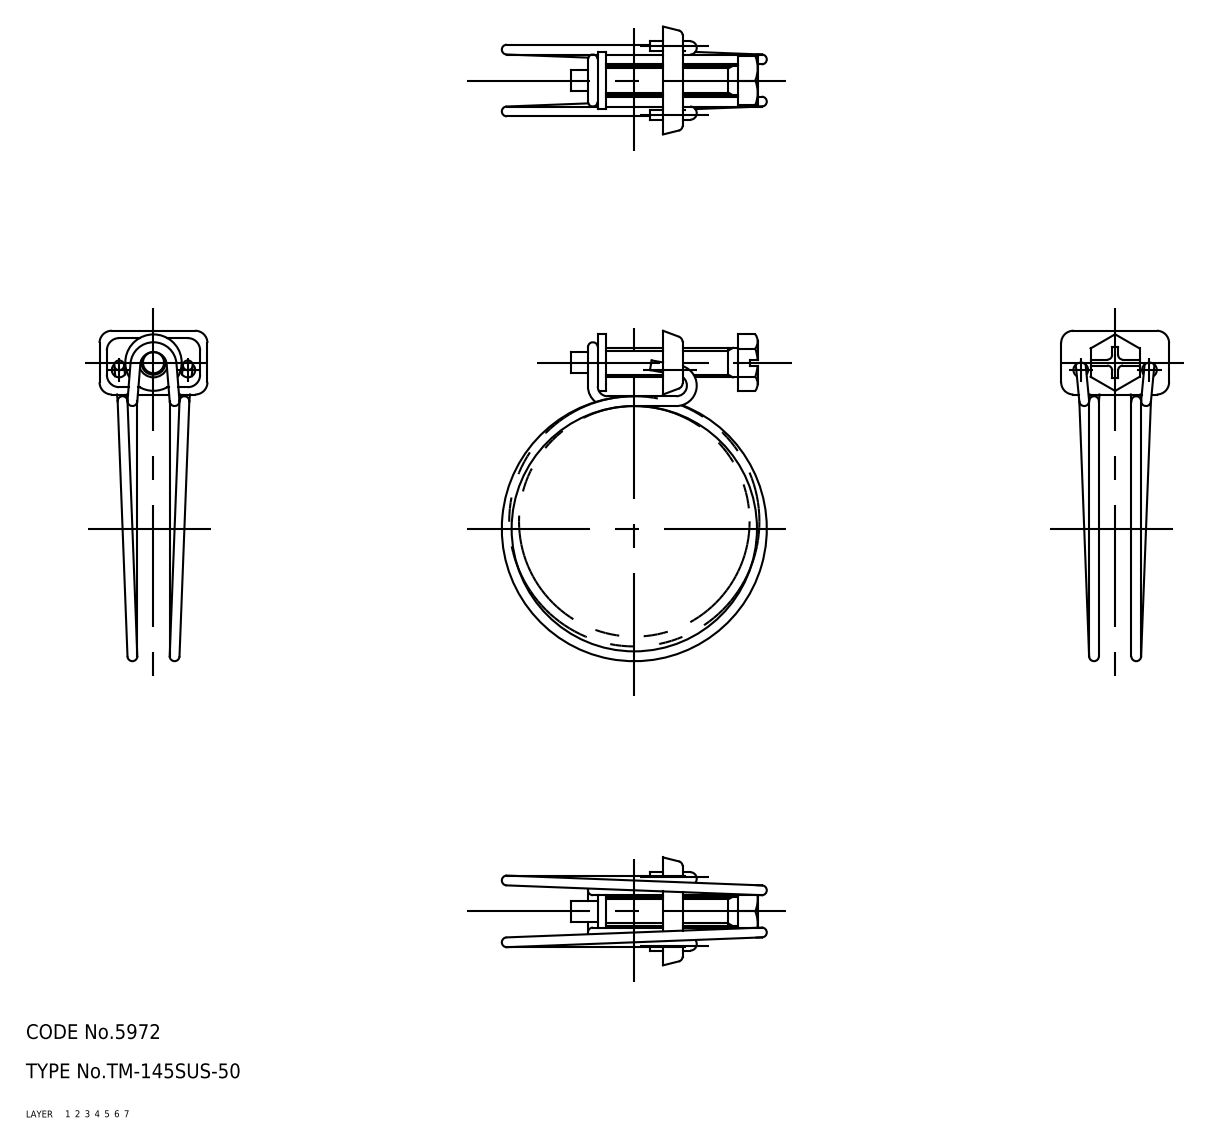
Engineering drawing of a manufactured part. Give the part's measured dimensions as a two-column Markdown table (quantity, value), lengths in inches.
| quantity | value |
| --- | --- |
| part name | screw; holder; band; TM_145SUS_50_22265_36 |
| STEP written by | CADfix (AUTOMOTIVE_DESIGN) |
| units | inches |
| bodies | 3 solids, 119 faces (0 planar, 0 cylindrical, 119 other) |
| overall size | 2.652 × 2.126 × 0.866 |
| volume | 0.191 in³ |
| surface area | 7.071 in² |
